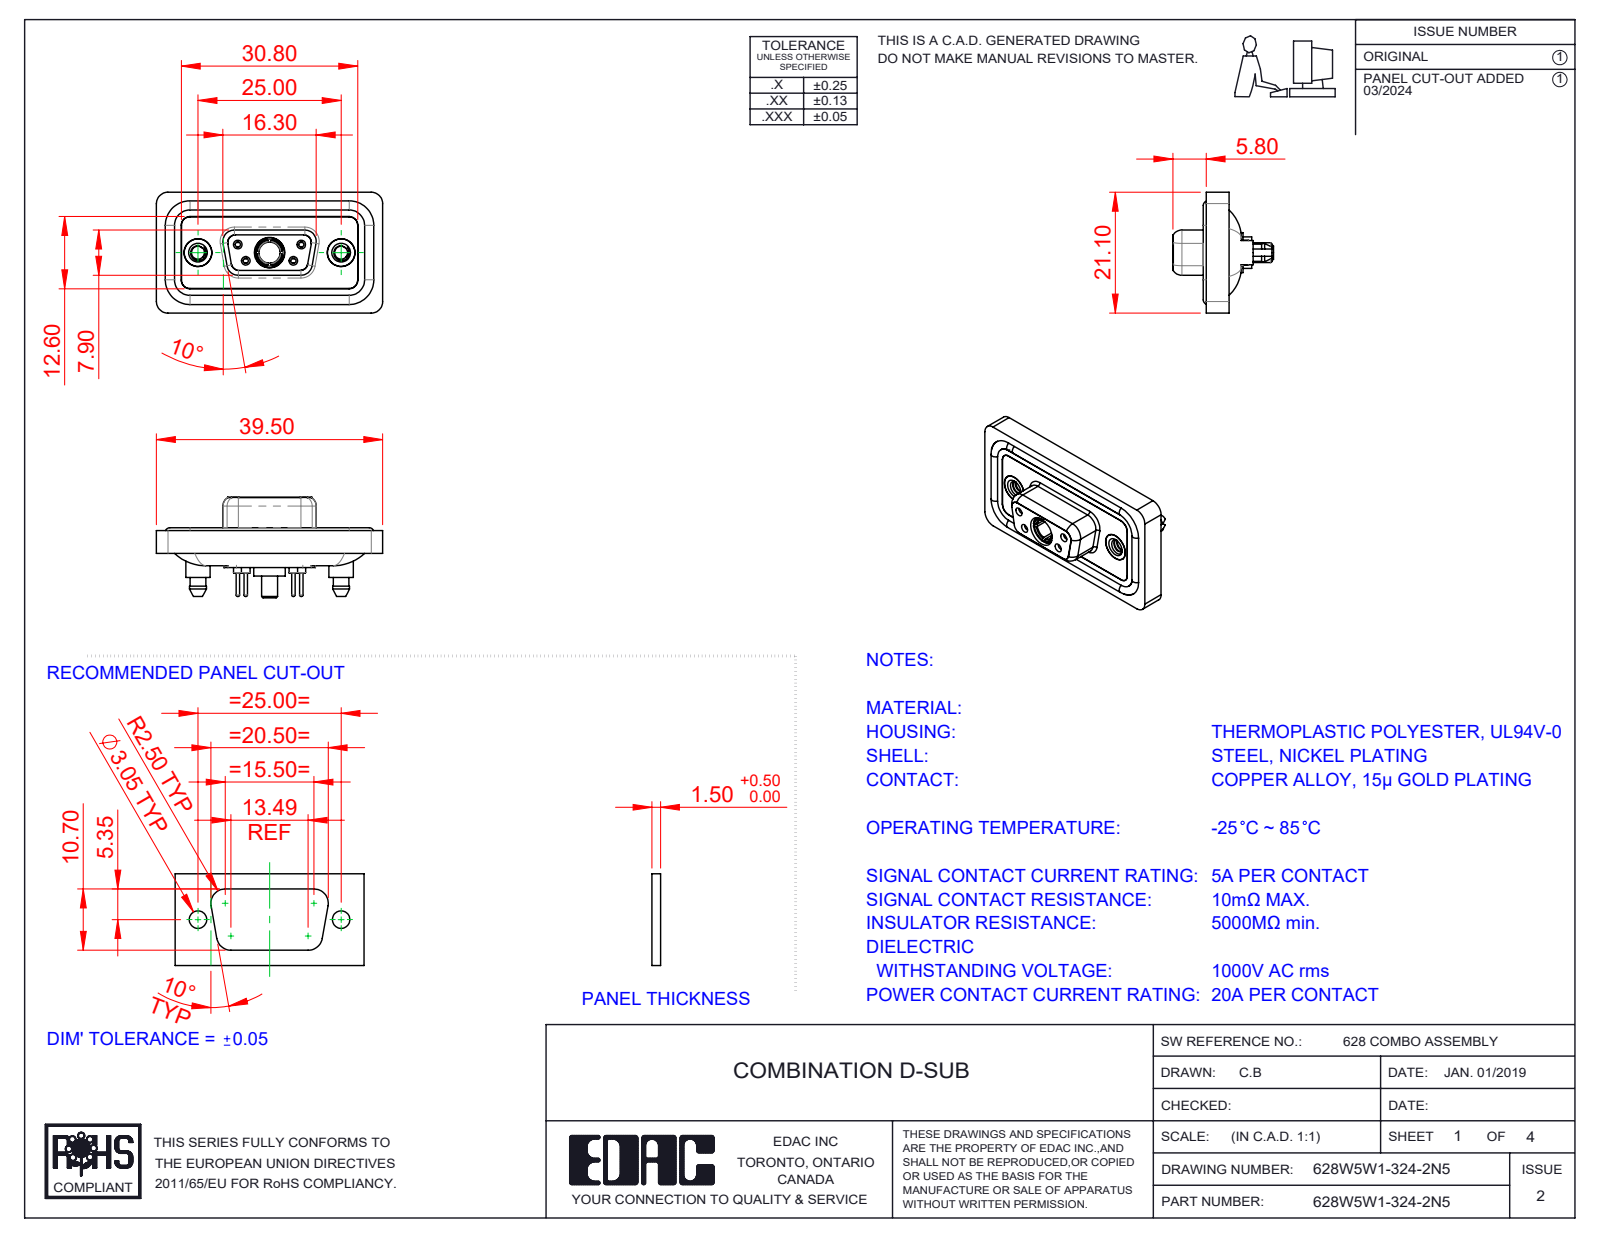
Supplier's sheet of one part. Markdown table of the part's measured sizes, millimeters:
| quantity | value |
| --- | --- |
| part name | 628Combo Shell Front_09 Contacts; 628Combo Housing_5W1; 628Combo Shell Rear_09 Contacts; Power Socket_20A S (+5 more) |
| STEP written by | SolidWorks 2023 (CONFIG_CONTROL_DESIGN) |
| units | millimeters |
| bodies | 13 solids, 730 faces (210 planar, 319 cylindrical, 201 other) |
| overall size | 39.5 × 21.1 × 17.55 |
| volume | 4 901 mm³ |
| surface area | 7 968 mm² |
| round holes (diameter × count) | 0.9 × 4, 1.1 × 4, 1.5 × 4, 2 × 4, 4.85 × 3, 1.6 × 2, 1.7 × 2, 2.26 × 2, 4 × 2, 4.05 × 2, 5 × 2, 3.7 × 1 |
| round bosses / shafts (diameter × count) | 1.6 × 6, 2.2 × 4, 0.6 × 4, 5.4 × 2, 4.95 × 2, 4.8 × 2, 4.25 × 2, 5.5 × 1 |
| partial cylindrical surfaces (radius × count) | 1.5 × 24, 2 × 18, 1.6 × 10, 1.35 × 8, 0.25 × 4, 0.5 × 4, 0.6 × 4, 0.65 × 4 |
| main face-to-face distances | 0.4, 2.9, 1.1, 1.8, 1.6, 0.5, 5.65, 7.45, 5.35, 3.6 |
| hole center spacings | 3.16, 5.72, 7.1, 12.5, 18.1, 4.39, 4.4, 8.31 |
